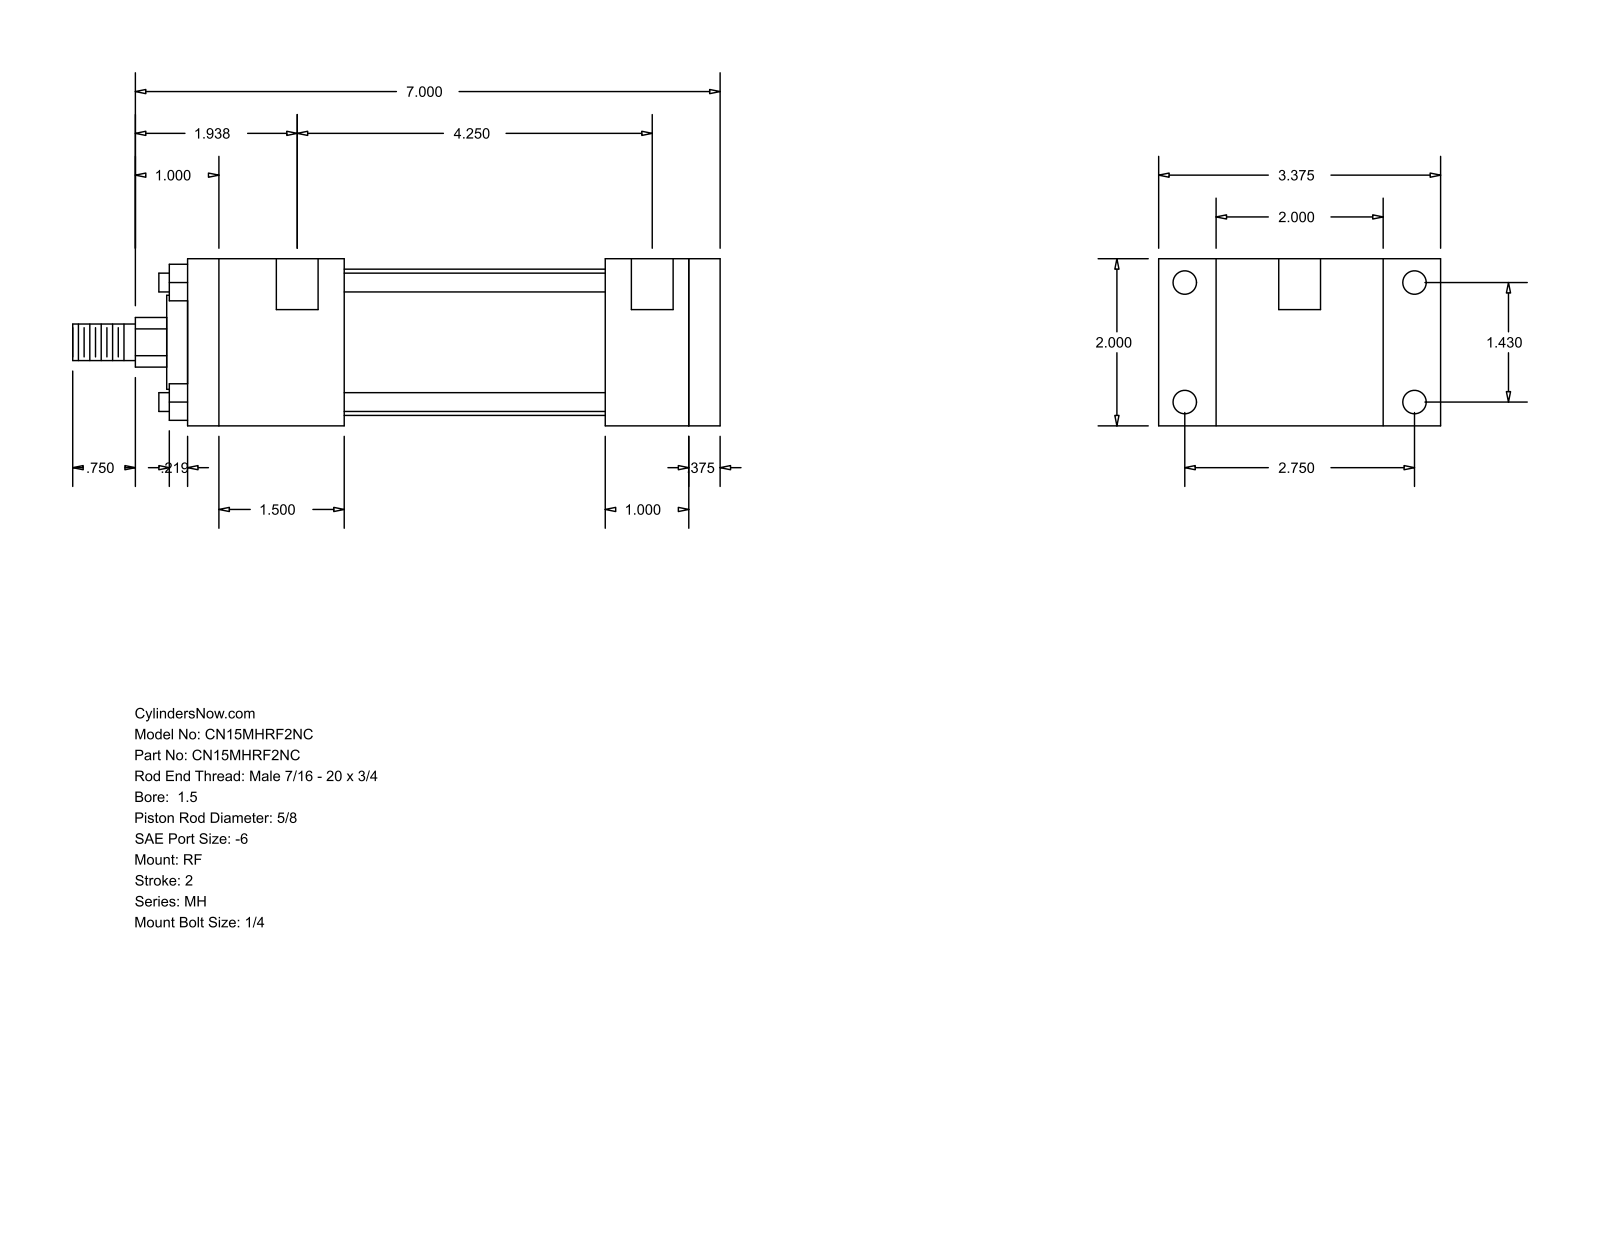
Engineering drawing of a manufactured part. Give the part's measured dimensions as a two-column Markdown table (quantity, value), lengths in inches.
| quantity | value |
| --- | --- |
| part name | MH_RF__0150_0.625 |
| STEP written by | GSSL Pune (CONFIG_CONTROL_DESIGN) |
| units | inches |
| bodies | 0 solids, 92 faces (64 planar, 28 cylindrical, 0 other) |
| overall size | 7.75 × 3.375 × 2 |
| round holes (diameter × count) | 0.219 × 4, 0.281 × 4, 0.5 × 2 |
| round bosses / shafts (diameter × count) | 0.225 × 4, 1.75 × 1, 1.125 × 1, 0.625 × 1, 0.437 × 1 |
| partial cylindrical surfaces (radius × count) | 0.297 × 1 |
| main face-to-face distances | 2, 0.375, 6, 6.375, 1, 0.687, 2.687, 5, 1.375, 1.875 |
| hole center spacings | 1.43, 2.75, 3.099, 4.375, 0.125, 4.25 |
